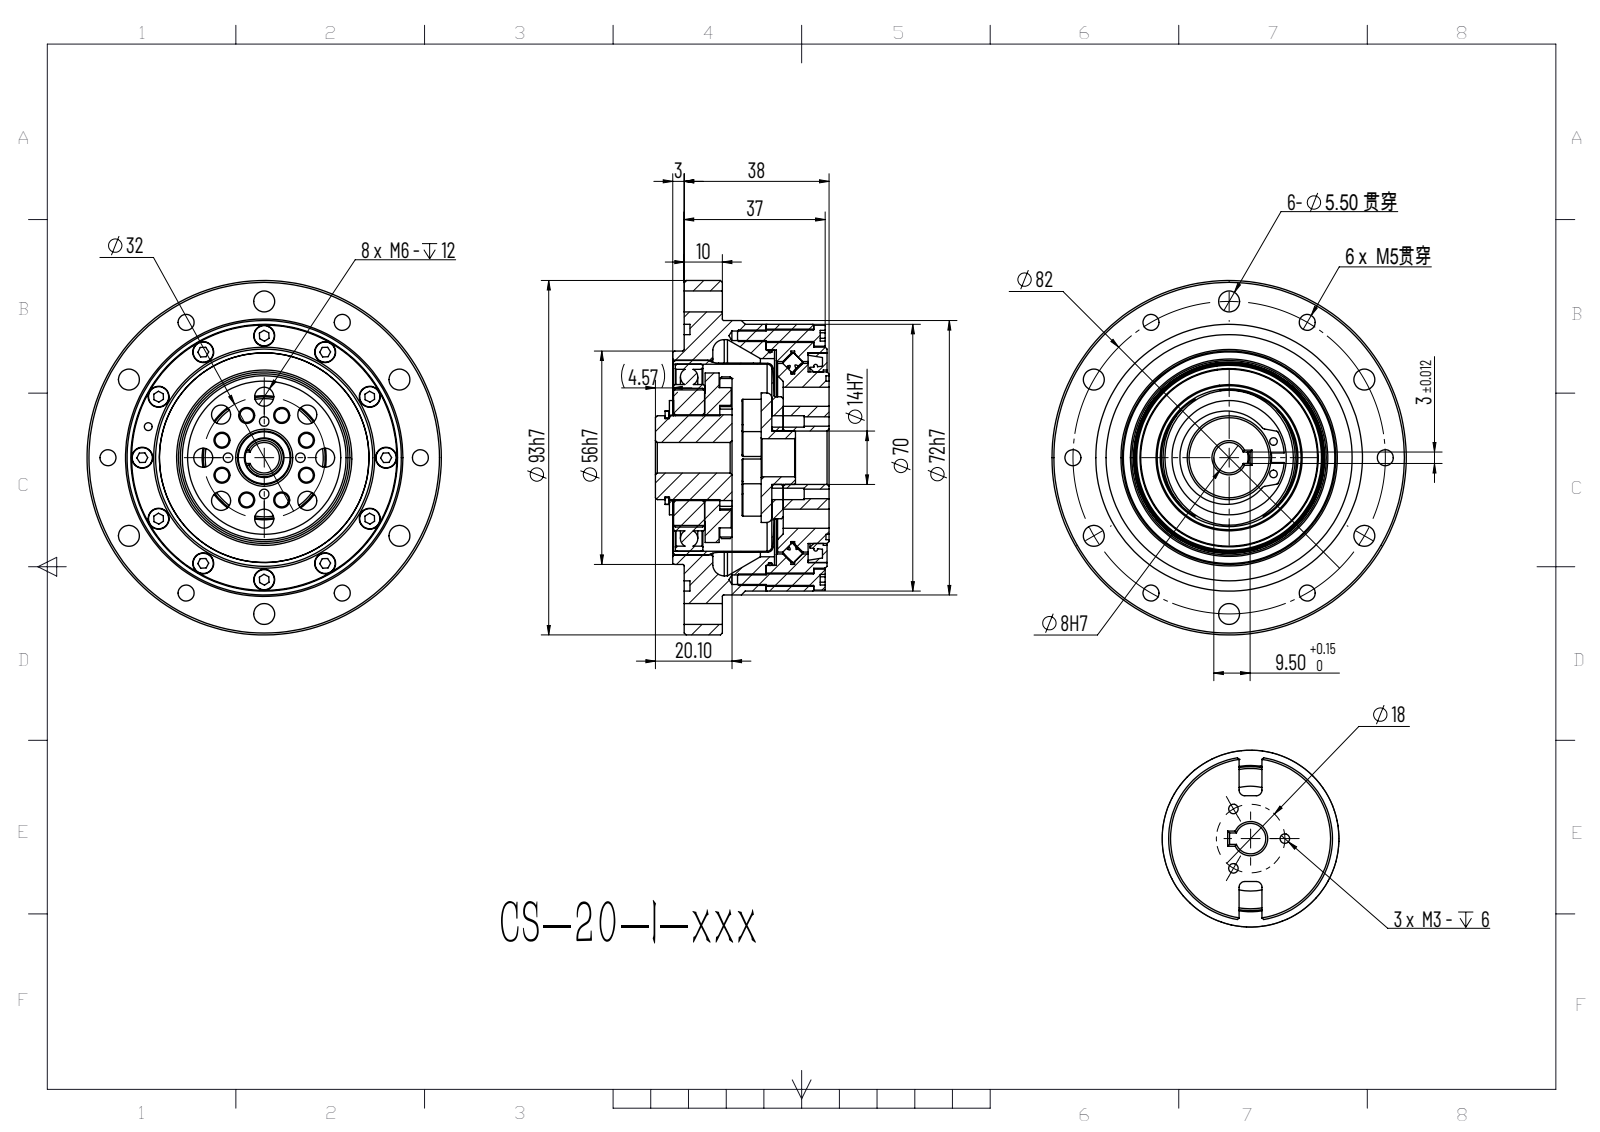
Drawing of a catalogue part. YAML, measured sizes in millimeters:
part_name: "CS-20-I; 3x10??; hexagon socket head cap screws gb_GB_FASTENER_SCREWS_HSHCS M5X16-C; hexagon socket head cap screws gb_GB_FASTENER_SCREWS_HSHCS M3X12-C (+8 more)"
step_written_by: "ONSHAPE BY PTC INC, 1.201 (AP242_MANAGED_MODEL_BASED_3D_ENGINEERING_MIM_LF)"
units: millimeters
bodies: {solids: 92, faces: 1125, planar: 578, cylindrical: 281, other: 266}
overall_size: [93, 93, 46.52]
volume: 136313
surface_area: 95220
round_holes:
  - {diameter: 2.5, count: 19}
  - {diameter: 3.5, count: 16}
  - {diameter: 4.2, count: 14}
  - {diameter: 5.5, count: 14}
  - {diameter: 5, count: 8}
  - {diameter: 3, count: 4}
  - {diameter: 3.2, count: 4}
  - {diameter: 2, count: 2}
  - {diameter: 8, count: 1}
  - {diameter: 10, count: 1}
  - {diameter: 14, count: 1}
  - {diameter: 20.5, count: 1}
round_bosses_or_shafts:
  - {diameter: 3, count: 70}
  - {diameter: 5.5, count: 16}
  - {diameter: 8.5, count: 8}
  - {diameter: 5, count: 8}
  - {diameter: 93, count: 1}
  - {diameter: 72, count: 1}
  - {diameter: 70, count: 1}
  - {diameter: 64.6, count: 1}
partial_cylinders:
  - {radius: 0.5, count: 2}
  - {radius: 1, count: 2}
  - {radius: 12.25, count: 2}
  - {radius: 14.5, count: 1}
face_to_face_distances: [5.5, 1.5, 21.5, 11, 10, 4, 7, 28.5, 18.5, 11.5]
hole_center_spacings: [41, 63.38, 20.8, 32, 52.01, 70.55, 37.32, 21.22]
